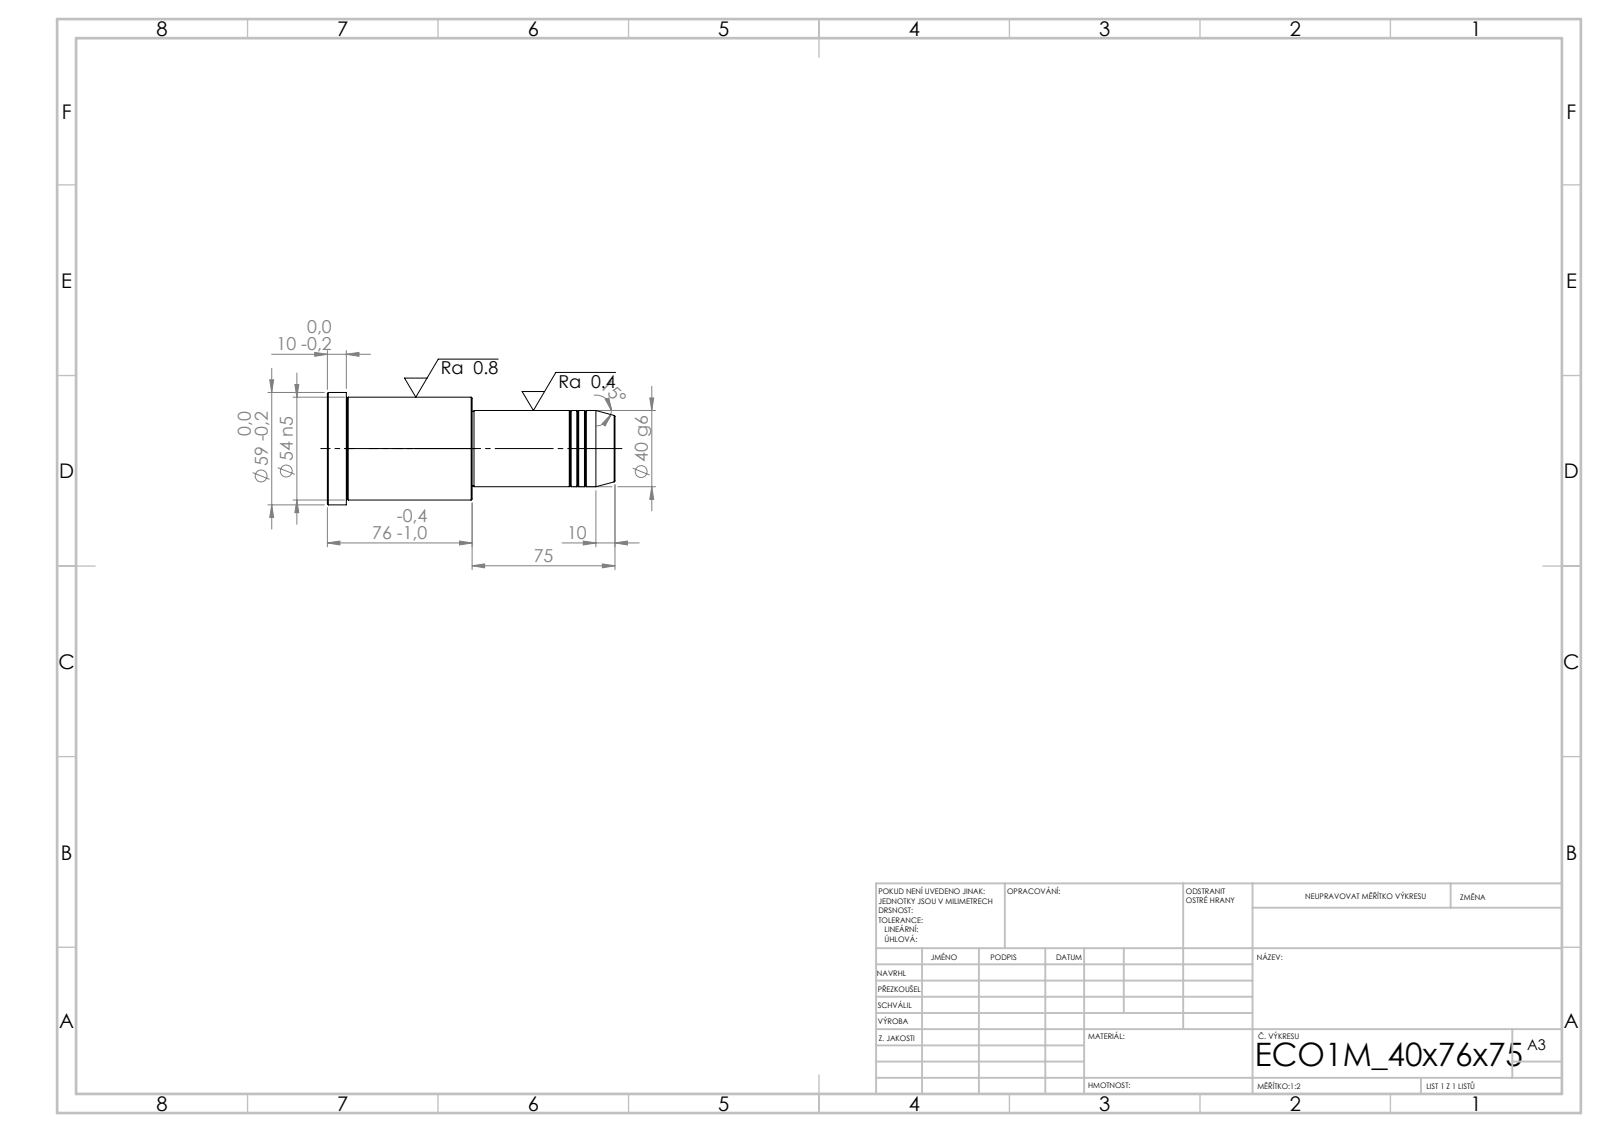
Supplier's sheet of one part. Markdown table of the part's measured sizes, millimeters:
| quantity | value |
| --- | --- |
| STEP written by | SolidWorks 2019 (CONFIG_CONTROL_DESIGN) |
| units | millimeters |
| bodies | 1 solid, 43 faces (5 planar, 14 cylindrical, 24 other) |
| overall size | 151 × 59 × 59 |
| volume | 270 812 mm³ |
| surface area | 27 889 mm² |
| round bosses / shafts (diameter × count) | 59 × 1, 54 × 1, 40 × 1, 39 × 1 |
| main face-to-face distances | 76, 75, 151, 141, 66, 10, 74, 1, 67, 77 |
